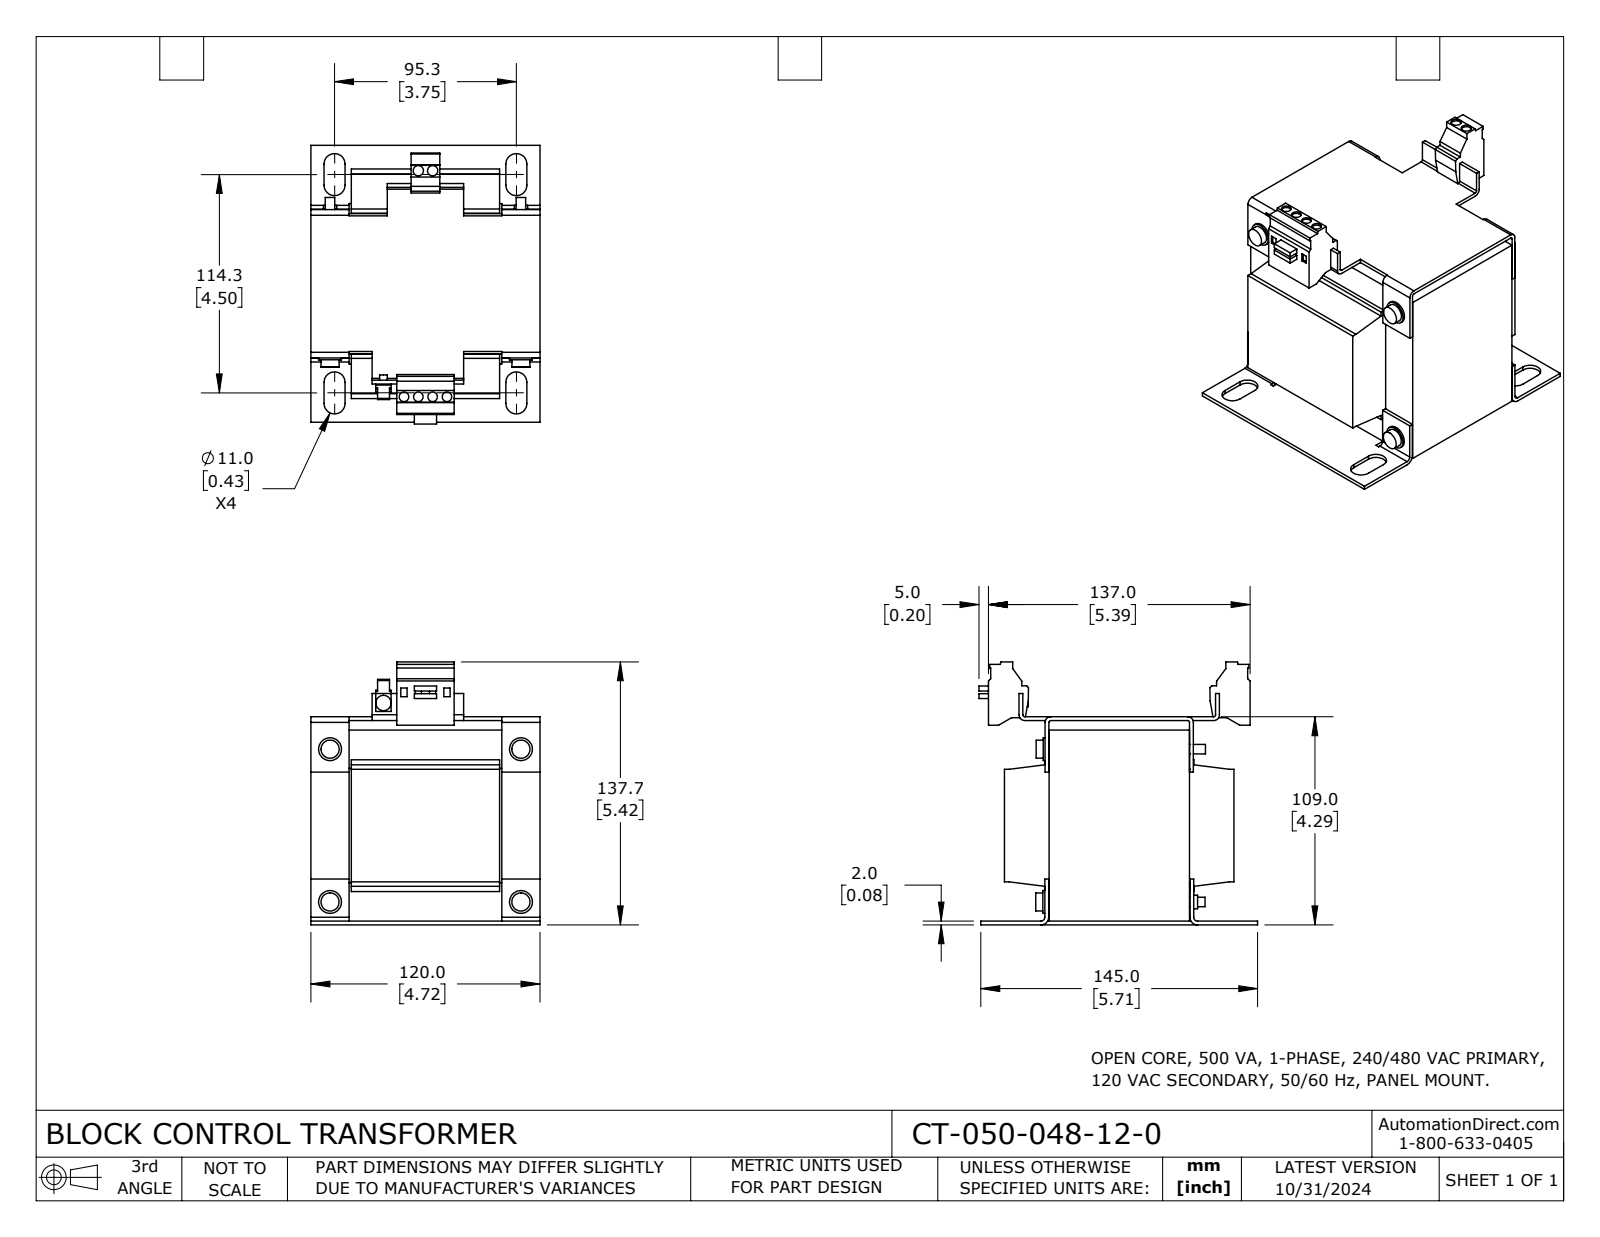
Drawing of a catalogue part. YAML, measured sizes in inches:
part_name: "CT-050-048-12-0"
step_written_by: "SolidWorks 2023 (CONFIG_CONTROL_DESIGN)"
units: inches
bodies: {solids: 1, faces: 327, planar: 235, cylindrical: 92, other: 0}
overall_size: [5.748, 5.421, 4.724]
volume: 71.74
surface_area: 241.9
round_holes:
  - {diameter: 0.197, count: 4}
  - {diameter: 0.213, count: 2}
round_bosses_or_shafts:
  - {diameter: 0.472, count: 4}
  - {diameter: 0.374, count: 4}
  - {diameter: 0.236, count: 4}
  - {diameter: 0.197, count: 4}
  - {diameter: 0.276, count: 2}
  - {diameter: 0.315, count: 1}
  - {diameter: 0.157, count: 1}
partial_cylinders:
  - {radius: 0.217, count: 8}
  - {radius: 0.039, count: 4}
  - {radius: 0.118, count: 4}
  - {radius: 0.079, count: 2}
  - {radius: 0.157, count: 2}
face_to_face_distances: [0.079, 4.213, 3.937, 0.787, 0.833, 3.892, 3.15, 0.197, 4.134, 4.291]
hole_center_spacings: [0.295, 4.671, 0.591, 4.661, 4.699, 0.886]
